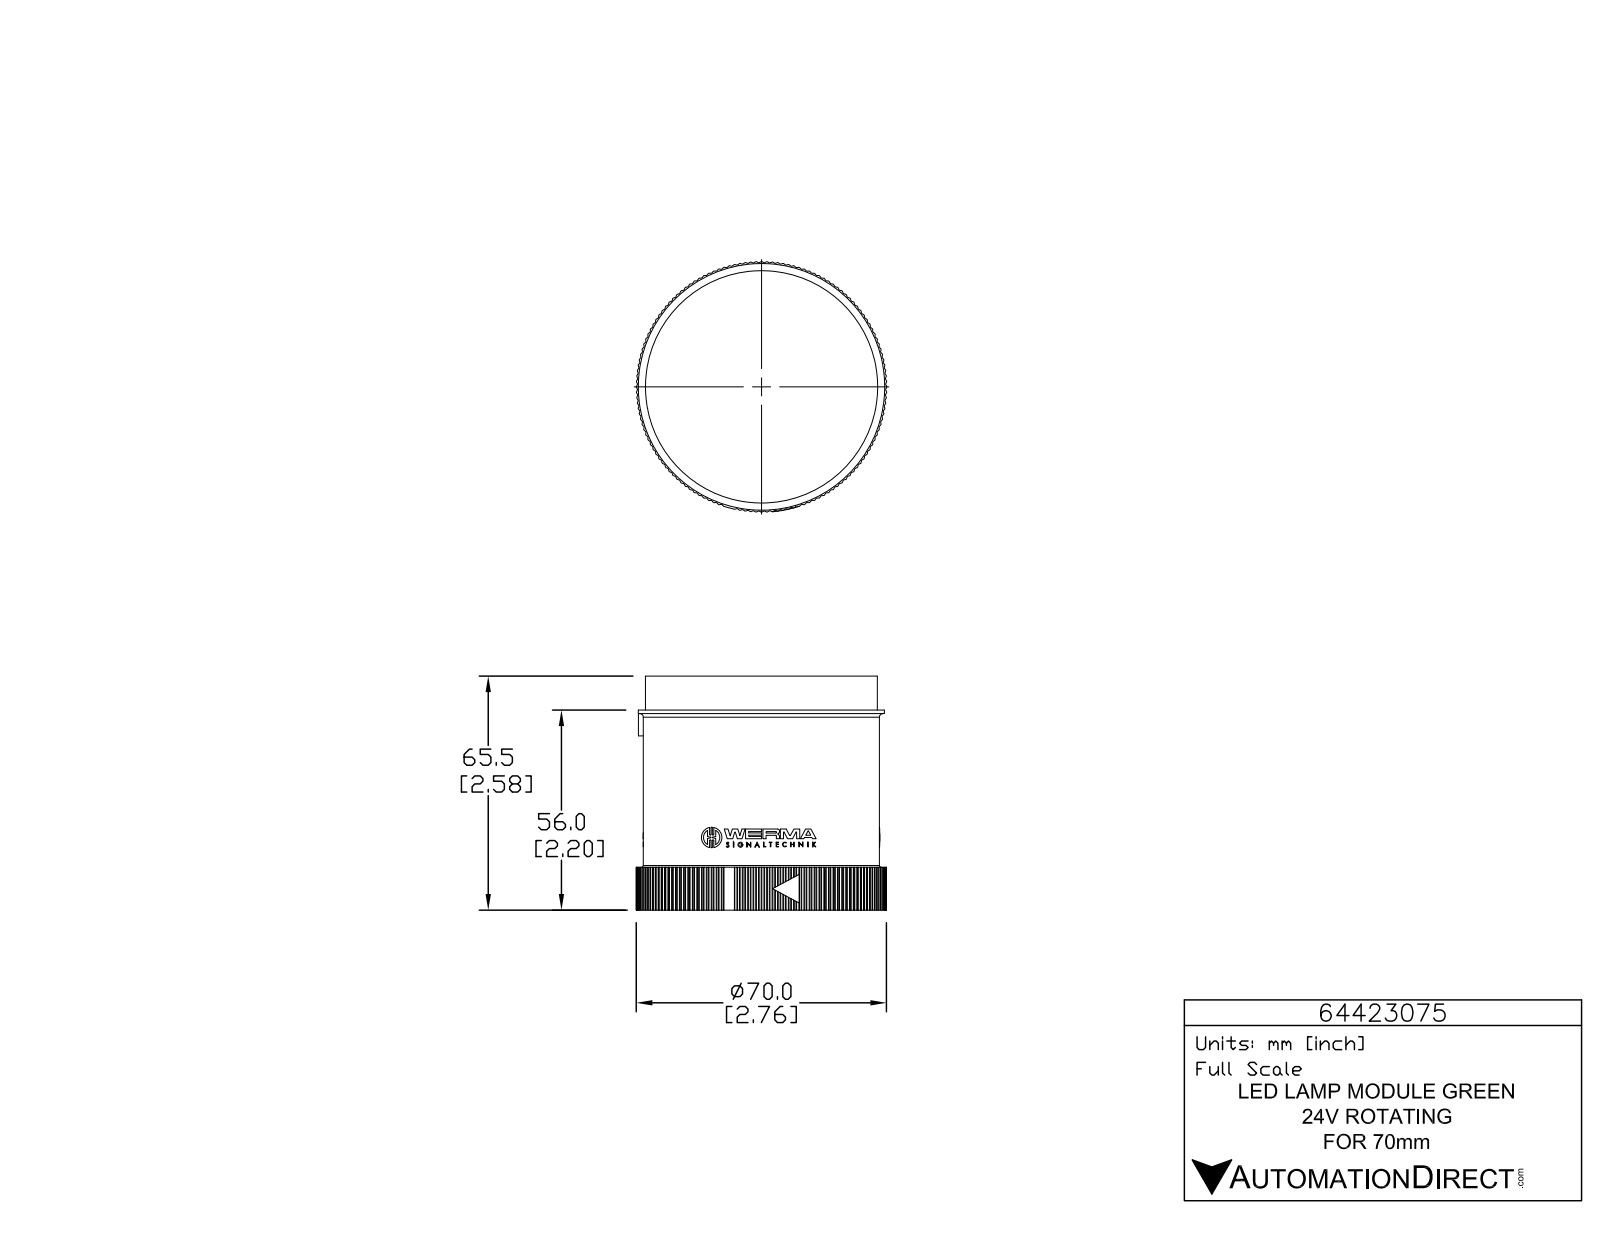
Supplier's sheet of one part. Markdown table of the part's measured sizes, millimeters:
| quantity | value |
| --- | --- |
| part name | 64423075 |
| STEP written by | SolidWorks 2015 (AUTOMOTIVE_DESIGN) |
| units | millimeters |
| bodies | 1 solid, 1400 faces (832 planar, 563 cylindrical, 5 other) |
| overall size | 70.2 × 70.2 × 65.5 |
| volume | 197 000 mm³ |
| surface area | 24 180 mm² |
| round holes (diameter × count) | 1 × 3, 65.4 × 1 |
| round bosses / shafts (diameter × count) | 5.7 × 3, 1.4 × 3, 69 × 1, 66.2 × 1, 65 × 1 |
| partial cylindrical surfaces (radius × count) | 0.2 × 285, 0.2 × 6, 0.2 × 6, 0.2 × 6, 3.3 × 6, 0.1 × 3, 0.1 × 3, 0.2 × 3 |
| main face-to-face distances | 55.9, 62.3, 9.6, 65.5, 56, 46.4, 9.5, 62.3, 12, 2.4 |
